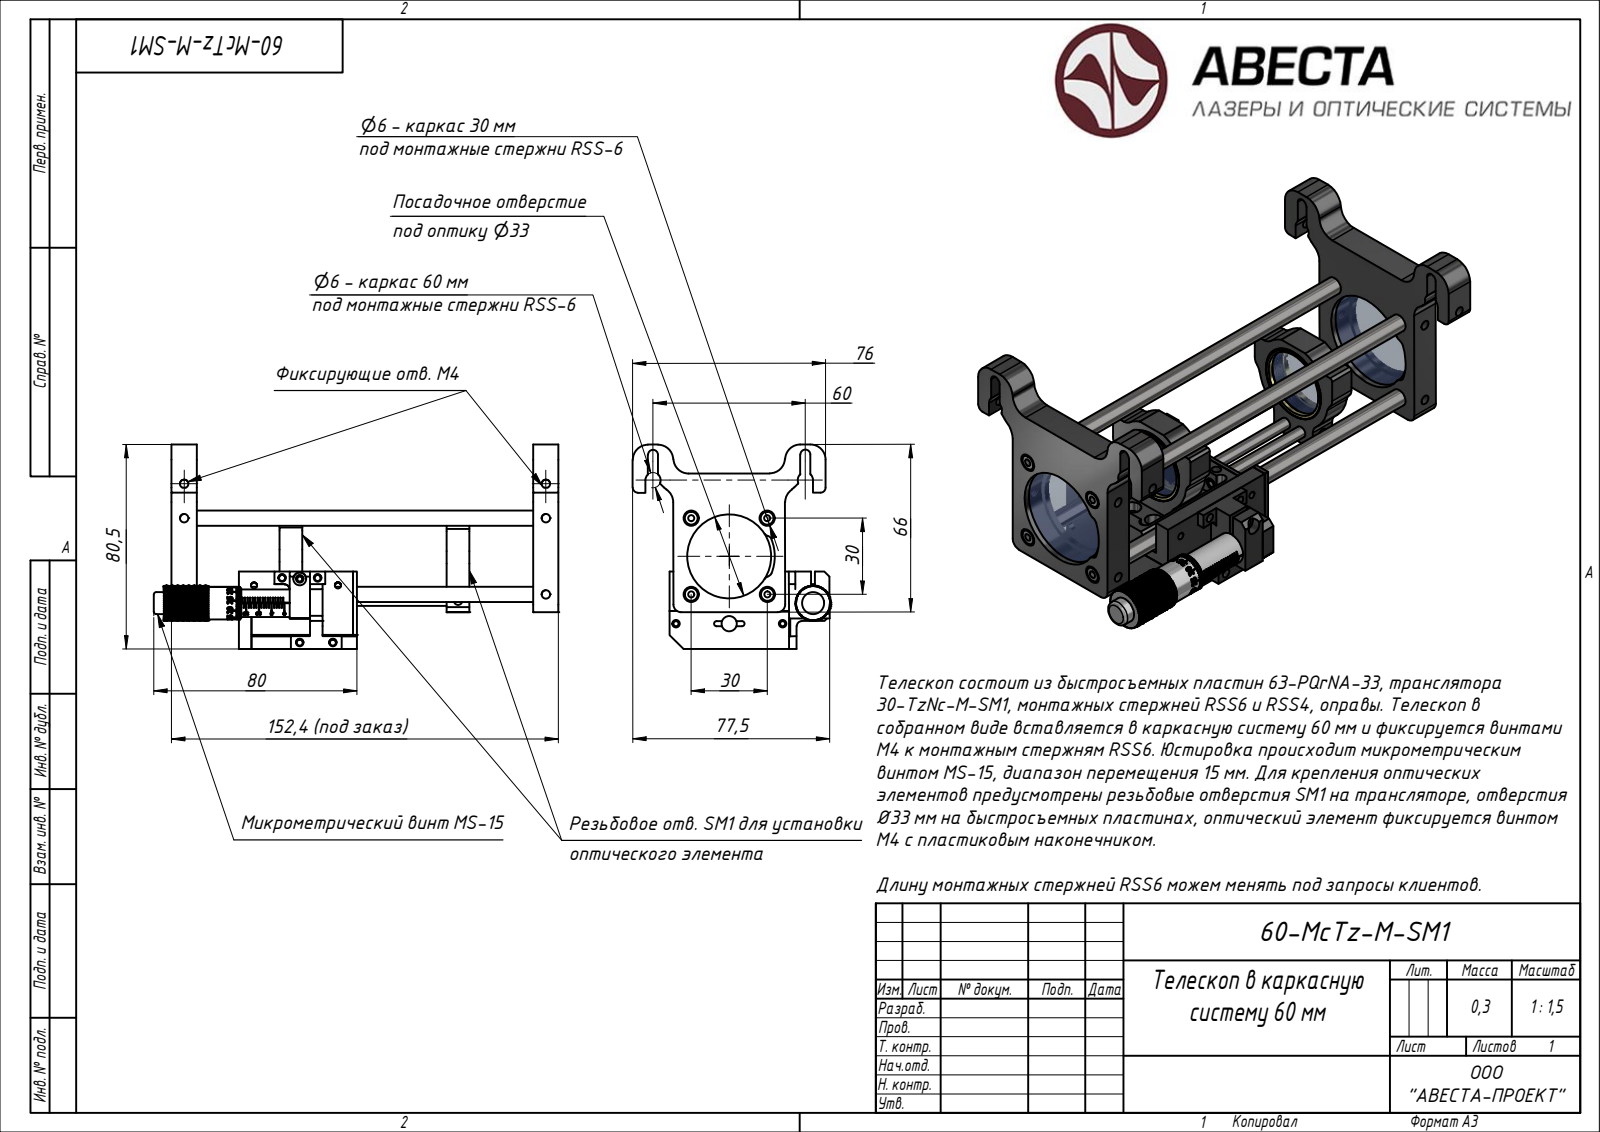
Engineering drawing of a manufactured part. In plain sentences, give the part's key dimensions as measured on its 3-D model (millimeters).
Its 3-D file was written by "Rhino 7.34 (AUTOMOTIVE_DESIGN)". It is 8 solids with 5733 faces: 3748 planar, 1304 cylindrical and 681 other. Overall it measures 300 by 82.06 by 78 millimeters. Its volume is 197 836 cubic millimeters and its surface area 109 342 square millimeters. Round holes: 31 of diameter 3.24, 18 of diameter 2.46, 15 of diameter 2.46, 11 of diameter 3, 11 of diameter 6, 8 of diameter 6.1, 6 of diameter 3.5, 5 of diameter 2.01, 2 of diameter 2.01, 2 of diameter 4, 2 of diameter 6.14, 1 of diameter 2. Round bosses or shafts: 4 of diameter 6, 2 of diameter 3, 1 of diameter 13.5, 1 of diameter 12.7, 1 of diameter 10.8, 1 of diameter 9.5, 1 of diameter 8.66. Partial cylindrical surfaces (rounded edges, fillets, slot ends): 20 of radius 0.12, 20 of radius 0.3, 20 of radius 5, 15 of radius 2, 14 of radius 4, 10 of radius 0.14, 10 of radius 0.14, 10 of radius 0.16. The main face-to-face distances are 8, 292, 10, 5.5, 142.4, 300, 284, 9, 7, 1.5. The hole center spacings are 142.4, 30, 292, 15, 60, 77.15, 143.04, 143.19.
